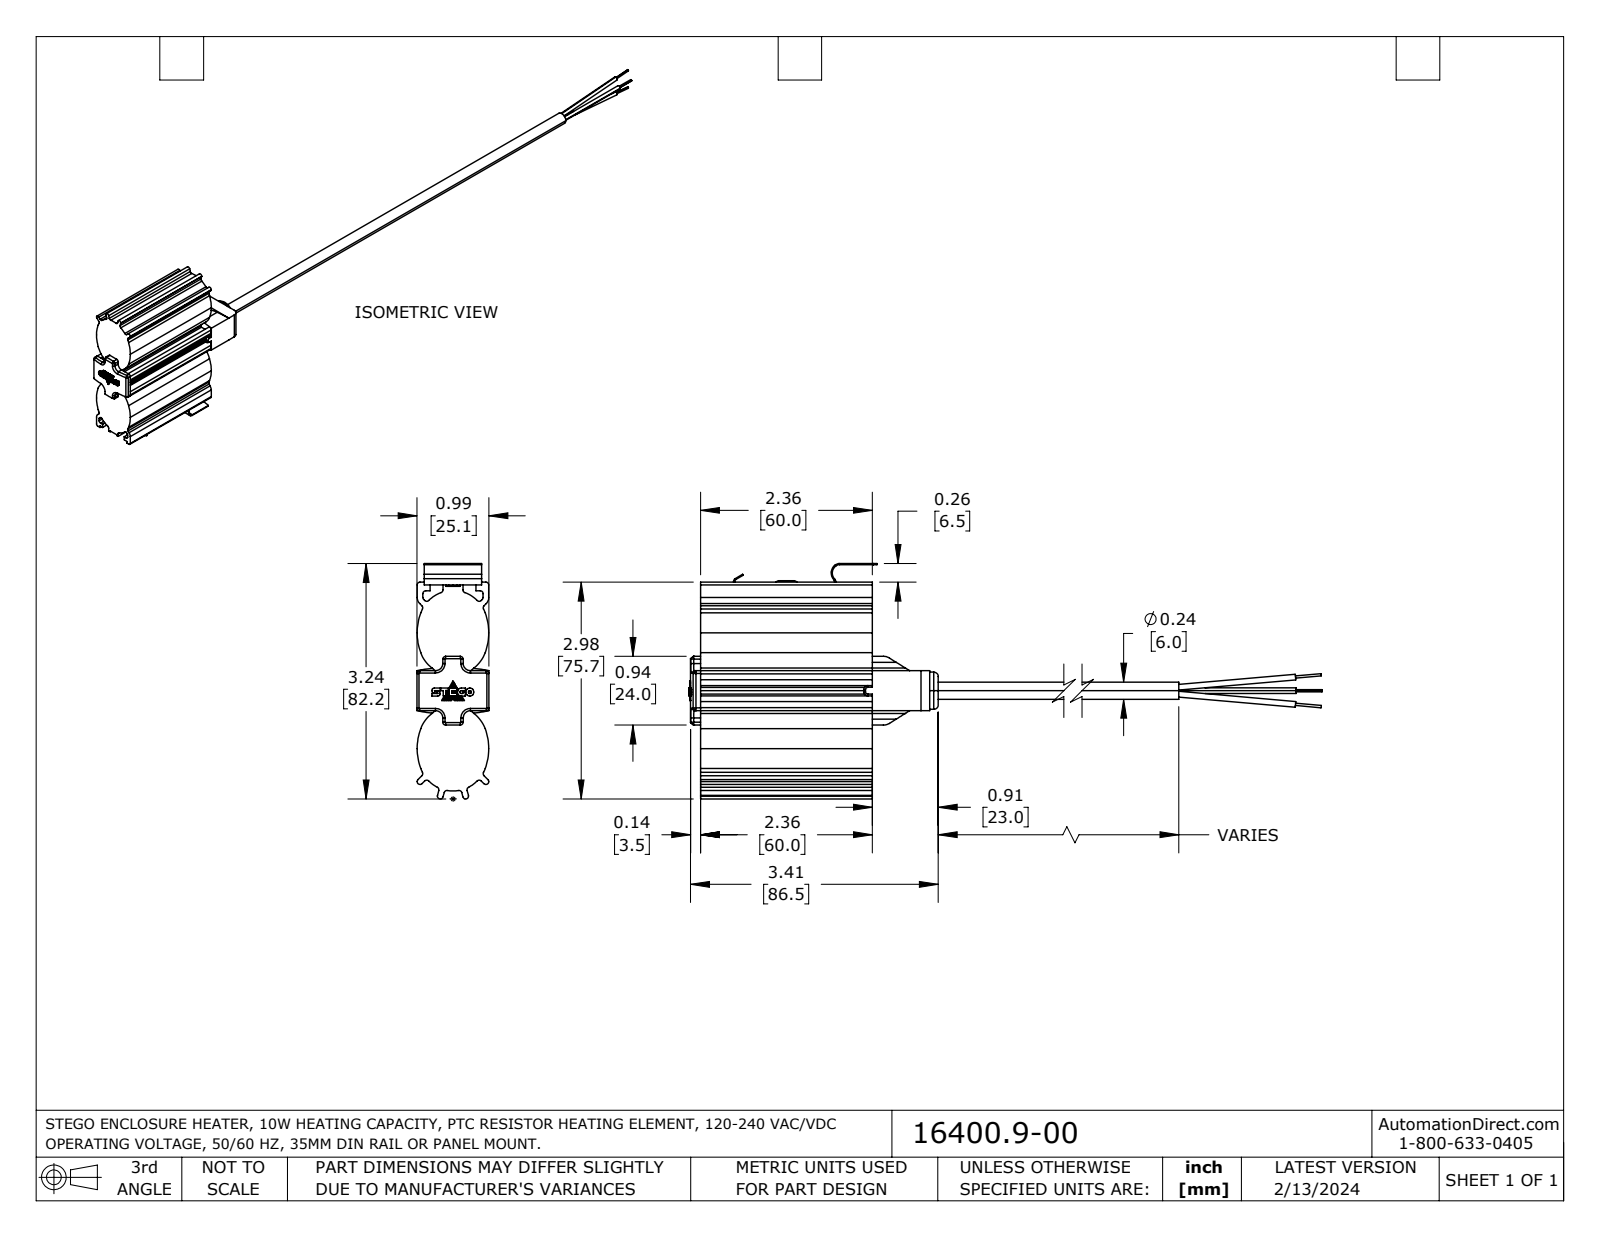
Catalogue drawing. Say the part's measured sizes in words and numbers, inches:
The part is named "2022_11_LPS164_3D_001_16400.0-00". Its 3-D file was written by "SolidWorks 2022 (AUTOMOTIVE_DESIGN)". It is 1 solid with 485 faces: 257 planar, 156 cylindrical and 72 other. Overall it measures 15.177 by 3.236 by 0.988 inches. Its volume is 6.597 cubic inches and its surface area 48.63 square inches. Round holes: 1 of diameter 0.071, 1 of diameter 0.177. Round bosses or shafts: 3 of diameter 0.079, 3 of diameter 0.031, 1 of diameter 0.512, 1 of diameter 0.236, 1 of diameter 0.118. Partial cylindrical surfaces (rounded edges, fillets, slot ends): 32 of radius 0.039, 12 of radius 0.02, 8 of radius 0.079, 5 of radius 0.098, 4 of radius 0.043, 4 of radius 0.118, 4 of radius 0.157, 4 of radius 0.346. The main face-to-face distances are 2.362, 0.315, 0.016, 0.079, 0.118, 1.626, 1.61, 1.311, 1.295, 1.591.
